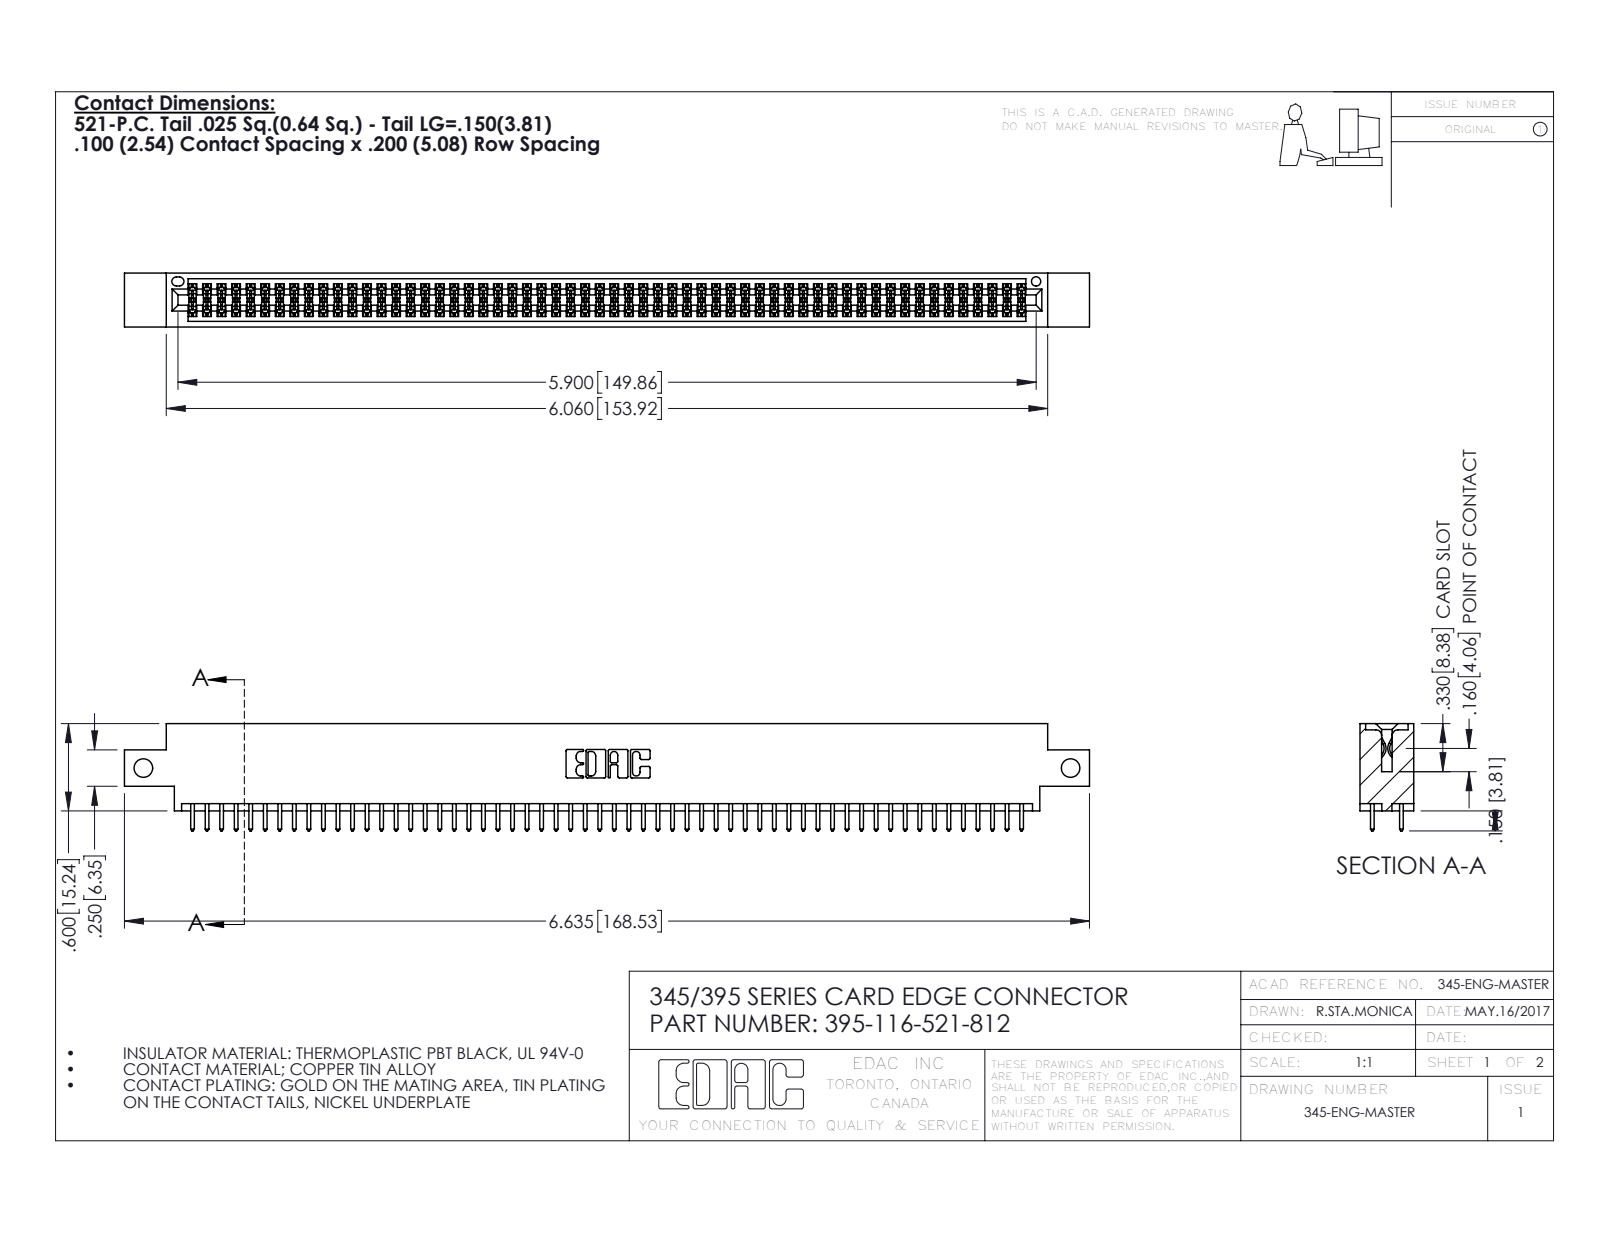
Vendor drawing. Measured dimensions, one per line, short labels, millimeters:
name: 345-292-001_345-293-121; 345 Part_0.170 Offset - Side Mount; 395-116-521-812
written by: SolidWorks 2016 (CONFIG_CONTROL_DESIGN)
unit: mm
bodies: 117 solids, 5930 faces (3912 planar, 2018 cylindrical, 0 other)
size: 168.5 × 18.7 × 9.4
volume: 16 300 mm³; area: 24 060 mm²
holes: 2× ⌀3.3, 1× ⌀1.6
rounds: 174× R0.2, 116× R0.3, 22× R0.3, 6× R0.2, 6× R0.8, 3× R0.7, 2× R0.4, 2× R0.5
face distances: 7.6, 1.8, 5.1, 9.4, 2.5, 6.9, 0.6, 5.7, 4.4, 3.8
hole spacings: 161.9
